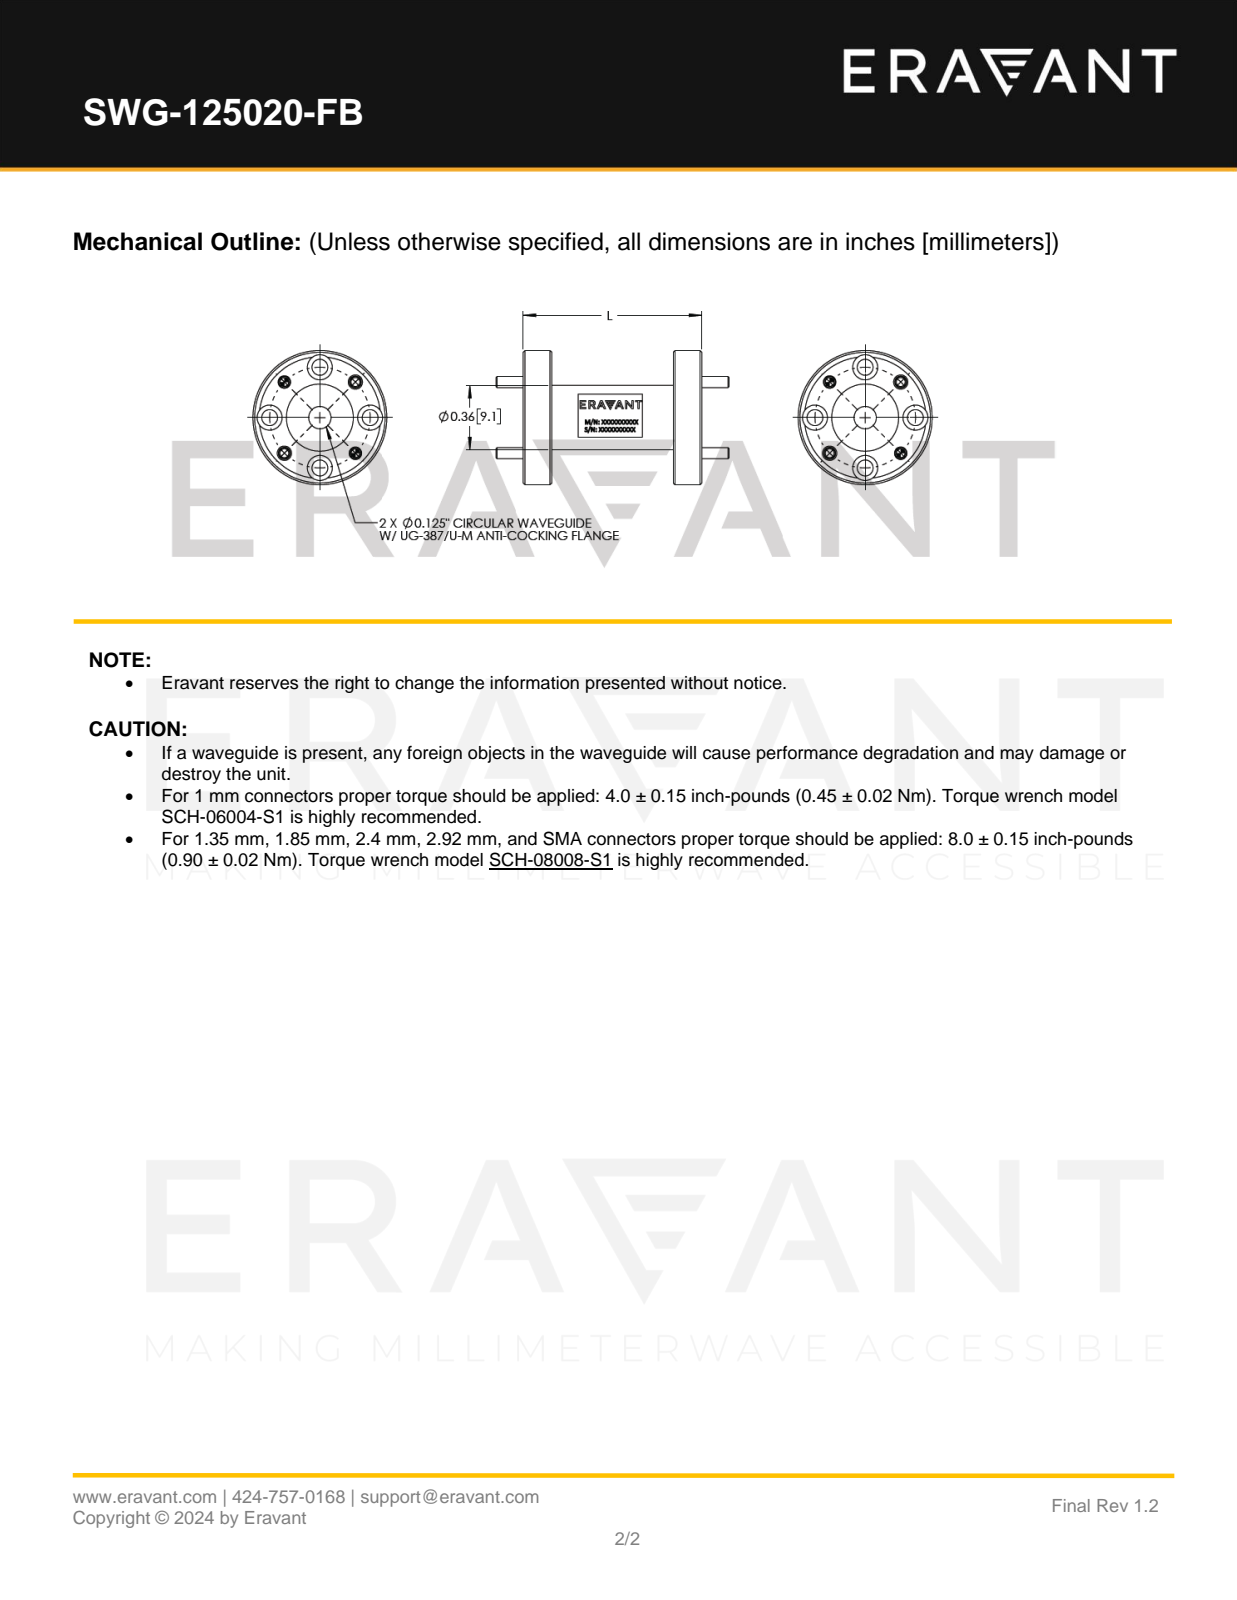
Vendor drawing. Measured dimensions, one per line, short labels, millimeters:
name: WG-FE-125-L DF
written by: SolidWorks 2016 (CONFIG_CONTROL_DESIGN)
unit: mm
bodies: 5 solids, 134 faces (24 planar, 70 cylindrical, 40 other)
size: 58.5 × 19.1 × 19.1
volume: 4 650 mm³; area: 3 052 mm²
holes: 4× ⌀1.5, 4× ⌀1.7, 4× ⌀2.3, 4× ⌀3.6, 1× ⌀3.2
bosses: 4× ⌀1.6, 1× ⌀19.1, 1× ⌀9.5, 1× ⌀9.1
face distances: 42.7, 49.3, 3.3, 46, 46, 3.3, 0.8, 50, 46.7, 4.1
hole spacings: 5.5, 10.1, 7.1, 13.2, 14.3, 13.2, 7.1, 14.3
